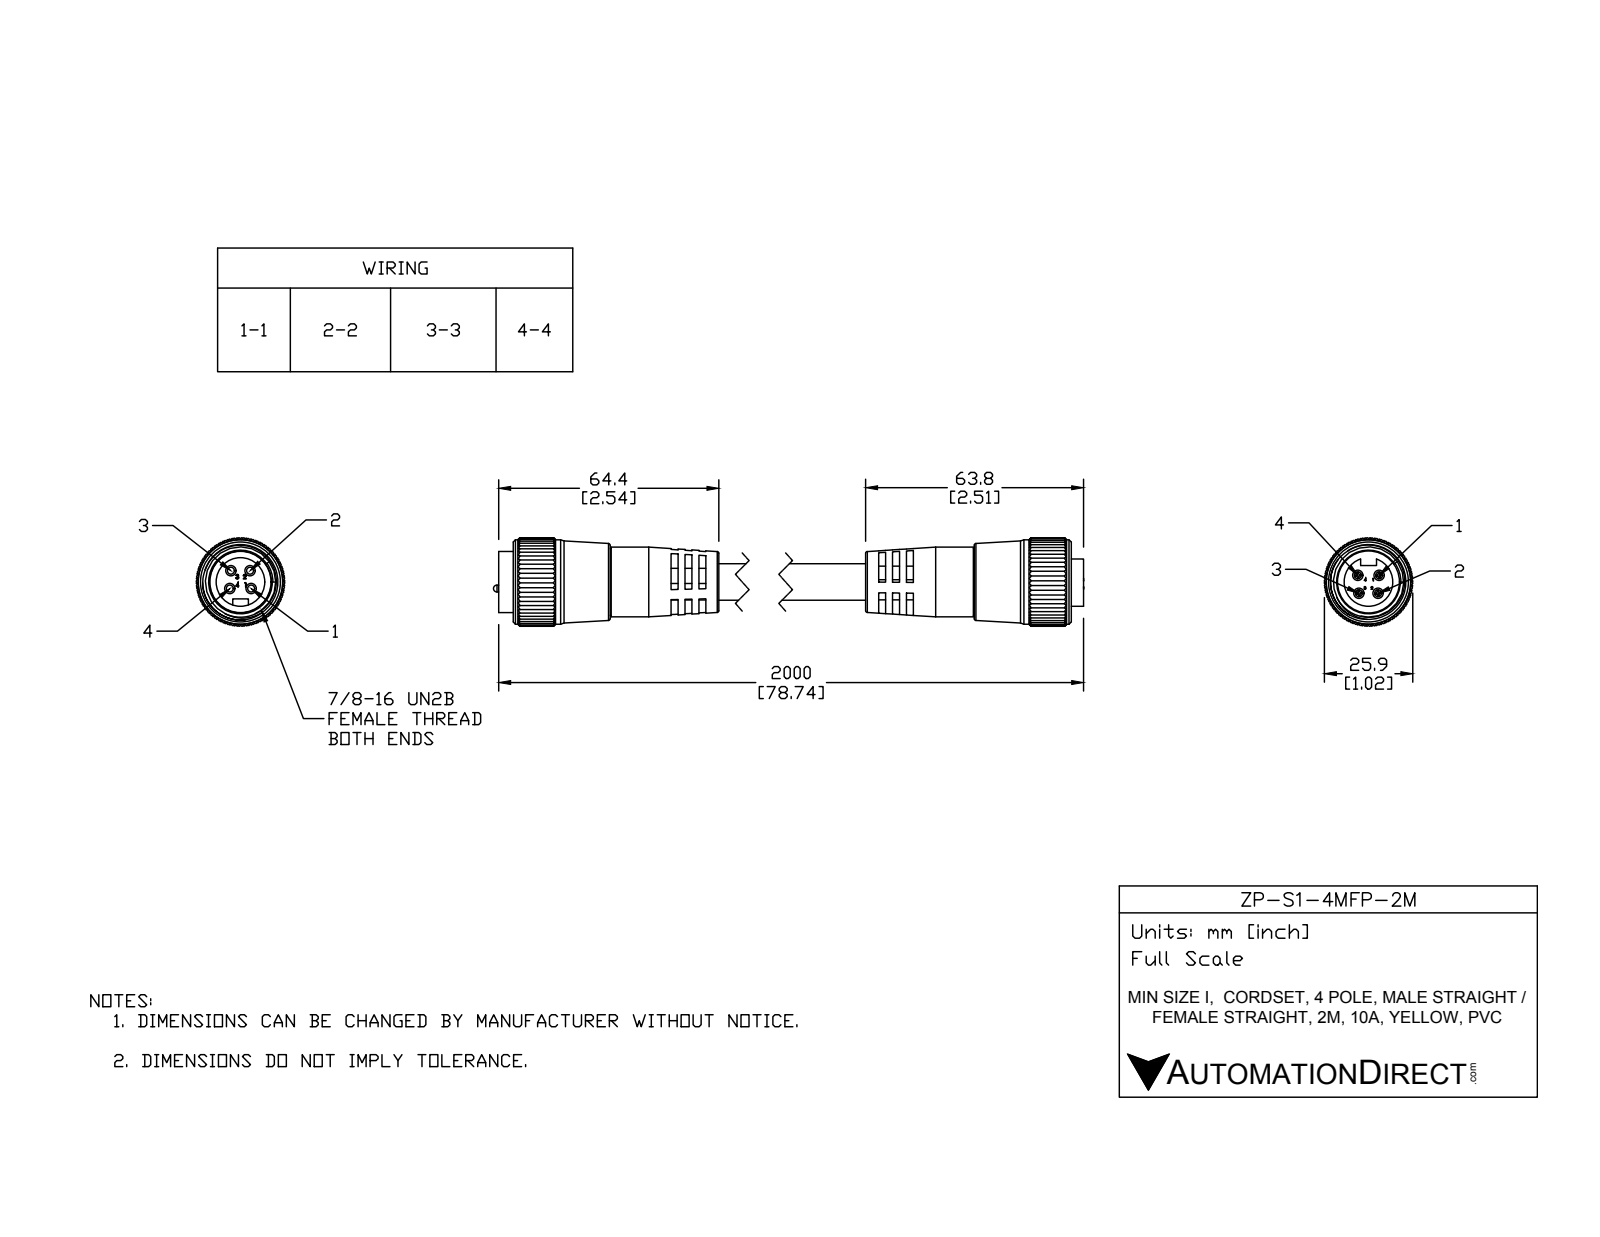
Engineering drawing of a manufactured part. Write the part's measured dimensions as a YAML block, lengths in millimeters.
part_name: "ZP-S1-4MFP-2M"
step_written_by: "SolidWorks 2015 (AUTOMOTIVE_DESIGN)"
units: millimeters
bodies: {solids: 8, faces: 1142, planar: 422, cylindrical: 624, other: 96}
overall_size: [229.66, 25.84, 25.83]
volume: 50831
surface_area: 23387
round_holes:
  - {diameter: 3.05, count: 4}
  - {diameter: 19.96, count: 1}
  - {diameter: 20.45, count: 1}
  - {diameter: 21, count: 1}
round_bosses_or_shafts:
  - {diameter: 3.05, count: 4}
  - {diameter: 2, count: 4}
  - {diameter: 24.68, count: 1}
  - {diameter: 20.4, count: 1}
  - {diameter: 19.5, count: 1}
  - {diameter: 17.88, count: 1}
  - {diameter: 14.22, count: 1}
  - {diameter: 9.91, count: 1}
partial_cylinders:
  - {radius: 0.25, count: 165}
  - {radius: 2.29, count: 1}
  - {radius: 5.25, count: 1}
  - {radius: 12.93, count: 1}
face_to_face_distances: [2, 4.02, 117.68, 113.65, 4.03, 125.74, 59.84, 4.04, 121.7, 121.72]
hole_center_spacings: [3.67, 5.24, 4.32, 4.33, 5.59, 6.24, 7.89, 7.9]
